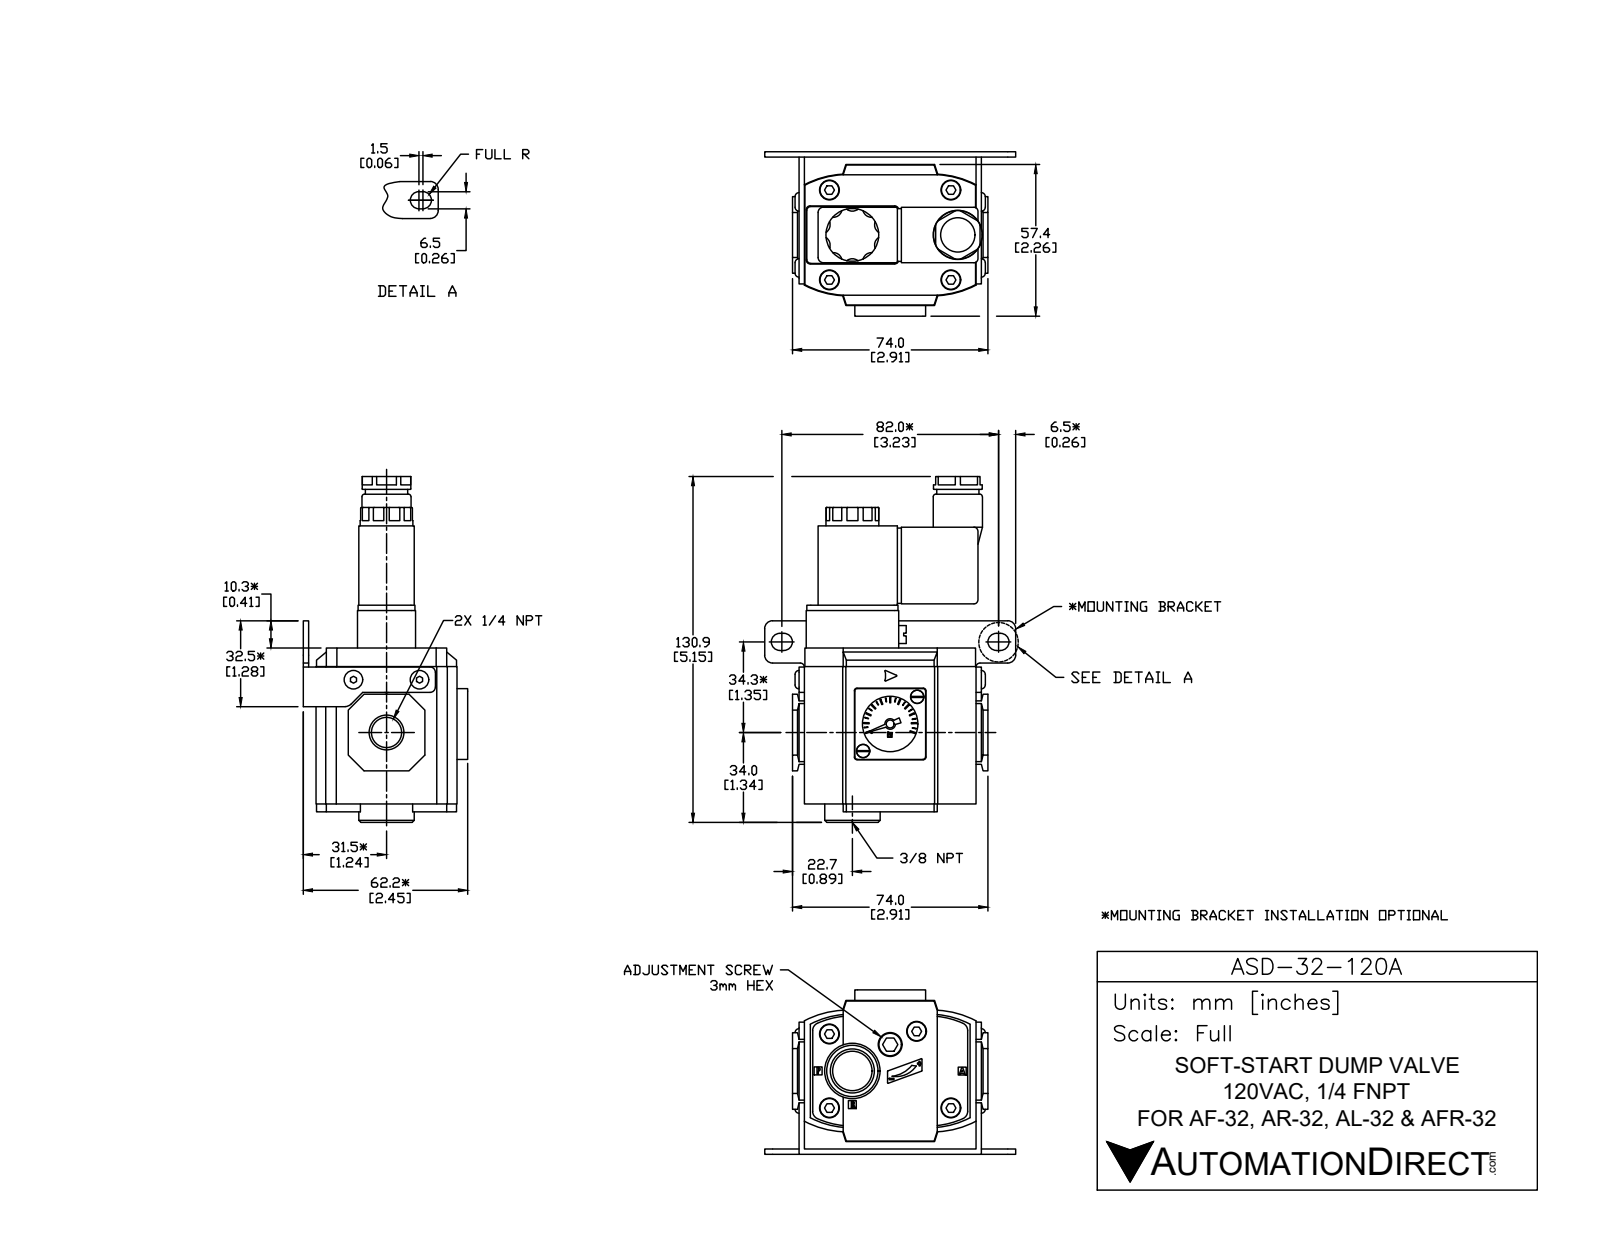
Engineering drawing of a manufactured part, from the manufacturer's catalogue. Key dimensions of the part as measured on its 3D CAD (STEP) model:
Part name (STEP PRODUCT): ASD-32-120A
STEP written by: SolidWorks 2015 (CONFIG_CONTROL_DESIGN)
Units: millimetres
Bodies: 22 solids, 550 faces (343 planar, 164 cylindrical, 43 other)
Overall size (bounding box): 130.9 × 95 × 62.9
Volume: 256 716 mm³ · Surface area: 60 550 mm²
Round holes (diameter × count): ⌀4 ×8, ⌀7.5 ×8, ⌀3 ×2, ⌀21 ×2, ⌀8.5 ×1, ⌀9 ×1, ⌀11.13 ×1, ⌀13 ×1, ⌀14.95 ×1
Round bosses / shafts (diameter × count): ⌀7.1 ×8, ⌀2.5 ×2, ⌀20 ×1, ⌀18.6 ×1, ⌀18.4 ×1, ⌀16 ×1, ⌀4 ×1
Partial cylindrical surfaces — rounded edges, fillets, slot ends (radius × count): R1.5 ×10, R3.16 ×10, R1 ×6, R3 ×6, R0.73 ×4, R1.25 ×4, R3.25 ×4, R34.8 ×4
Main face-to-face distances: 3, 2, 52, 59, 7, 21, 13.2, 34.2, 16.2, 37.2
Hole centre spacings: 3, 31, 46, 46.1, 55.47, 14.5, 16.48, 17.2
